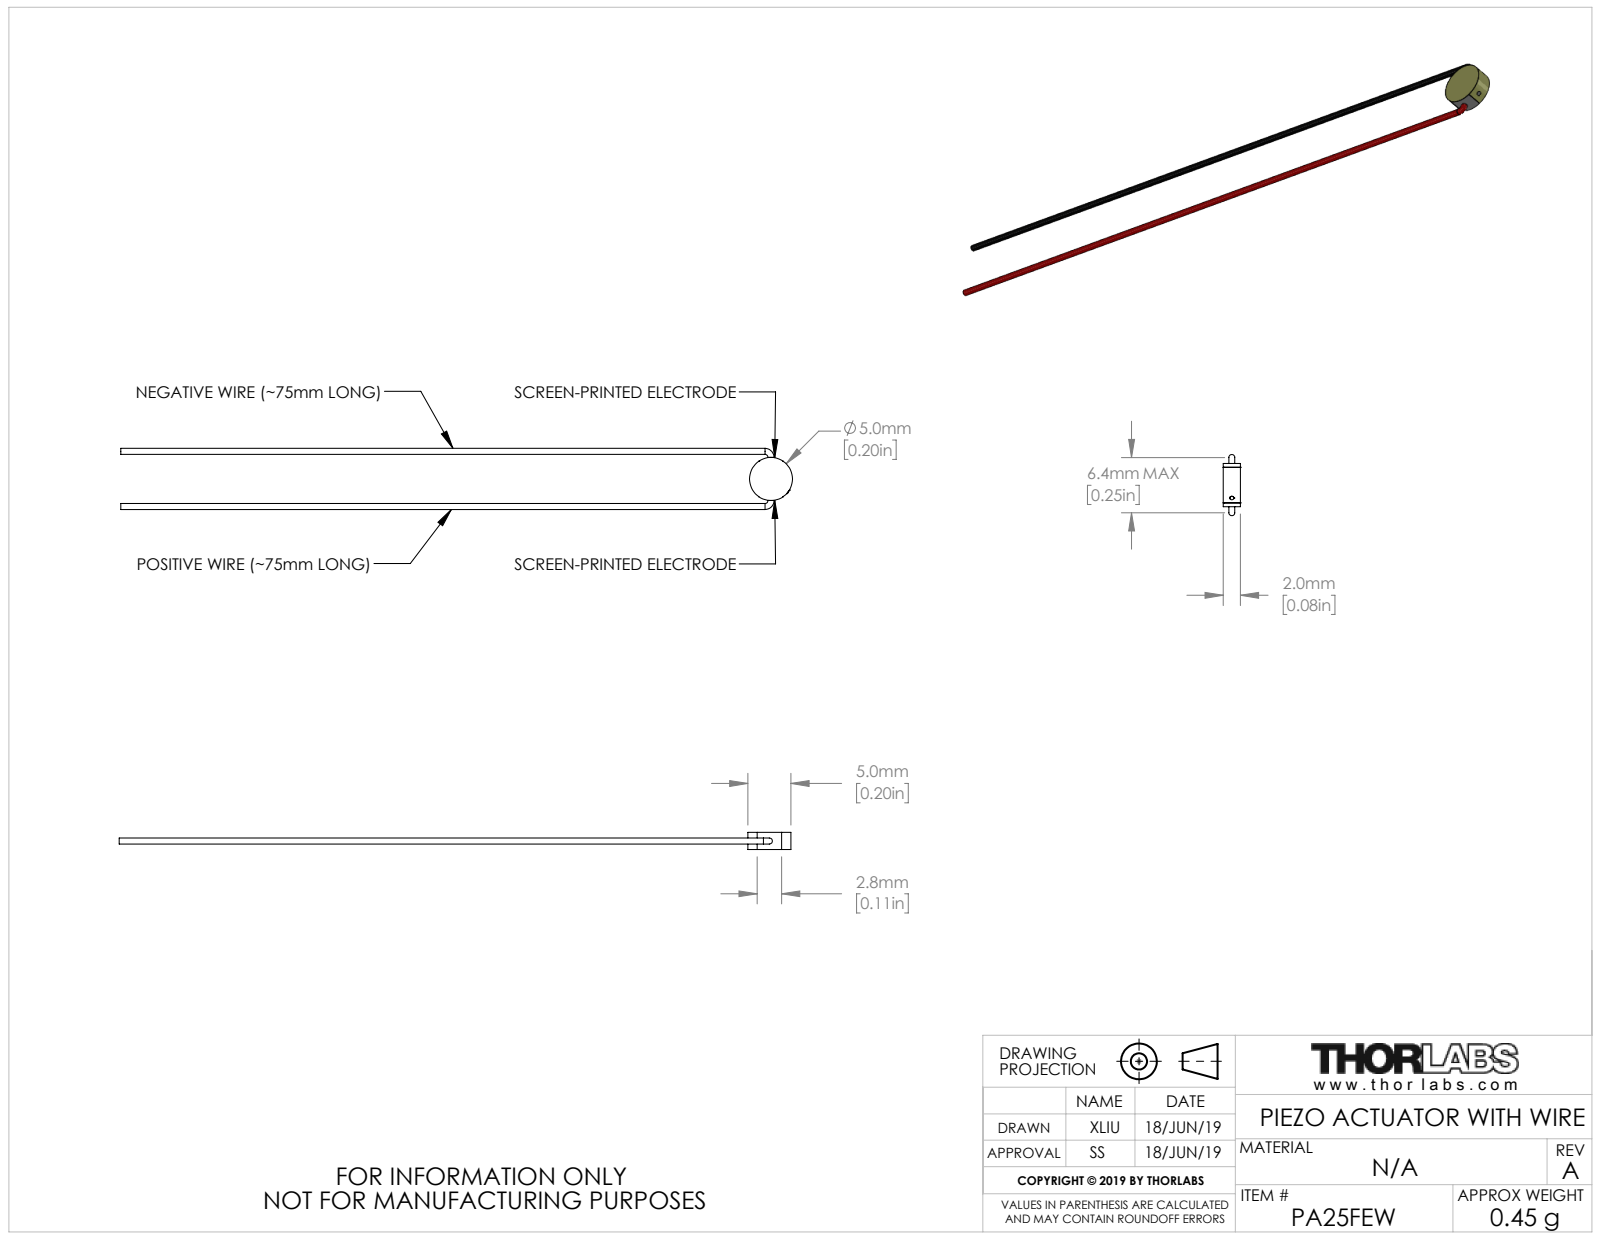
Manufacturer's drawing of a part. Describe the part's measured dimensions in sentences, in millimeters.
The part is named "CTN014120". Its 3-D file was written by "SolidWorks 2018 (AUTOMOTIVE_DESIGN)". It is 4 solids with 27 faces: 12 planar, 11 cylindrical and 4 other. Overall it measures 78.2 by 7.12 by 2 millimeters. Its volume is 98 cubic millimeters and its surface area 408 square millimeters. Round bosses or shafts: 2 of diameter 0.7, 1 of diameter 0.5. Partial cylindrical surfaces (rounded edges, fillets, slot ends): 1 of radius 2.5, 1 of radius 2.51. The main face-to-face distances are 2, 5.02.
